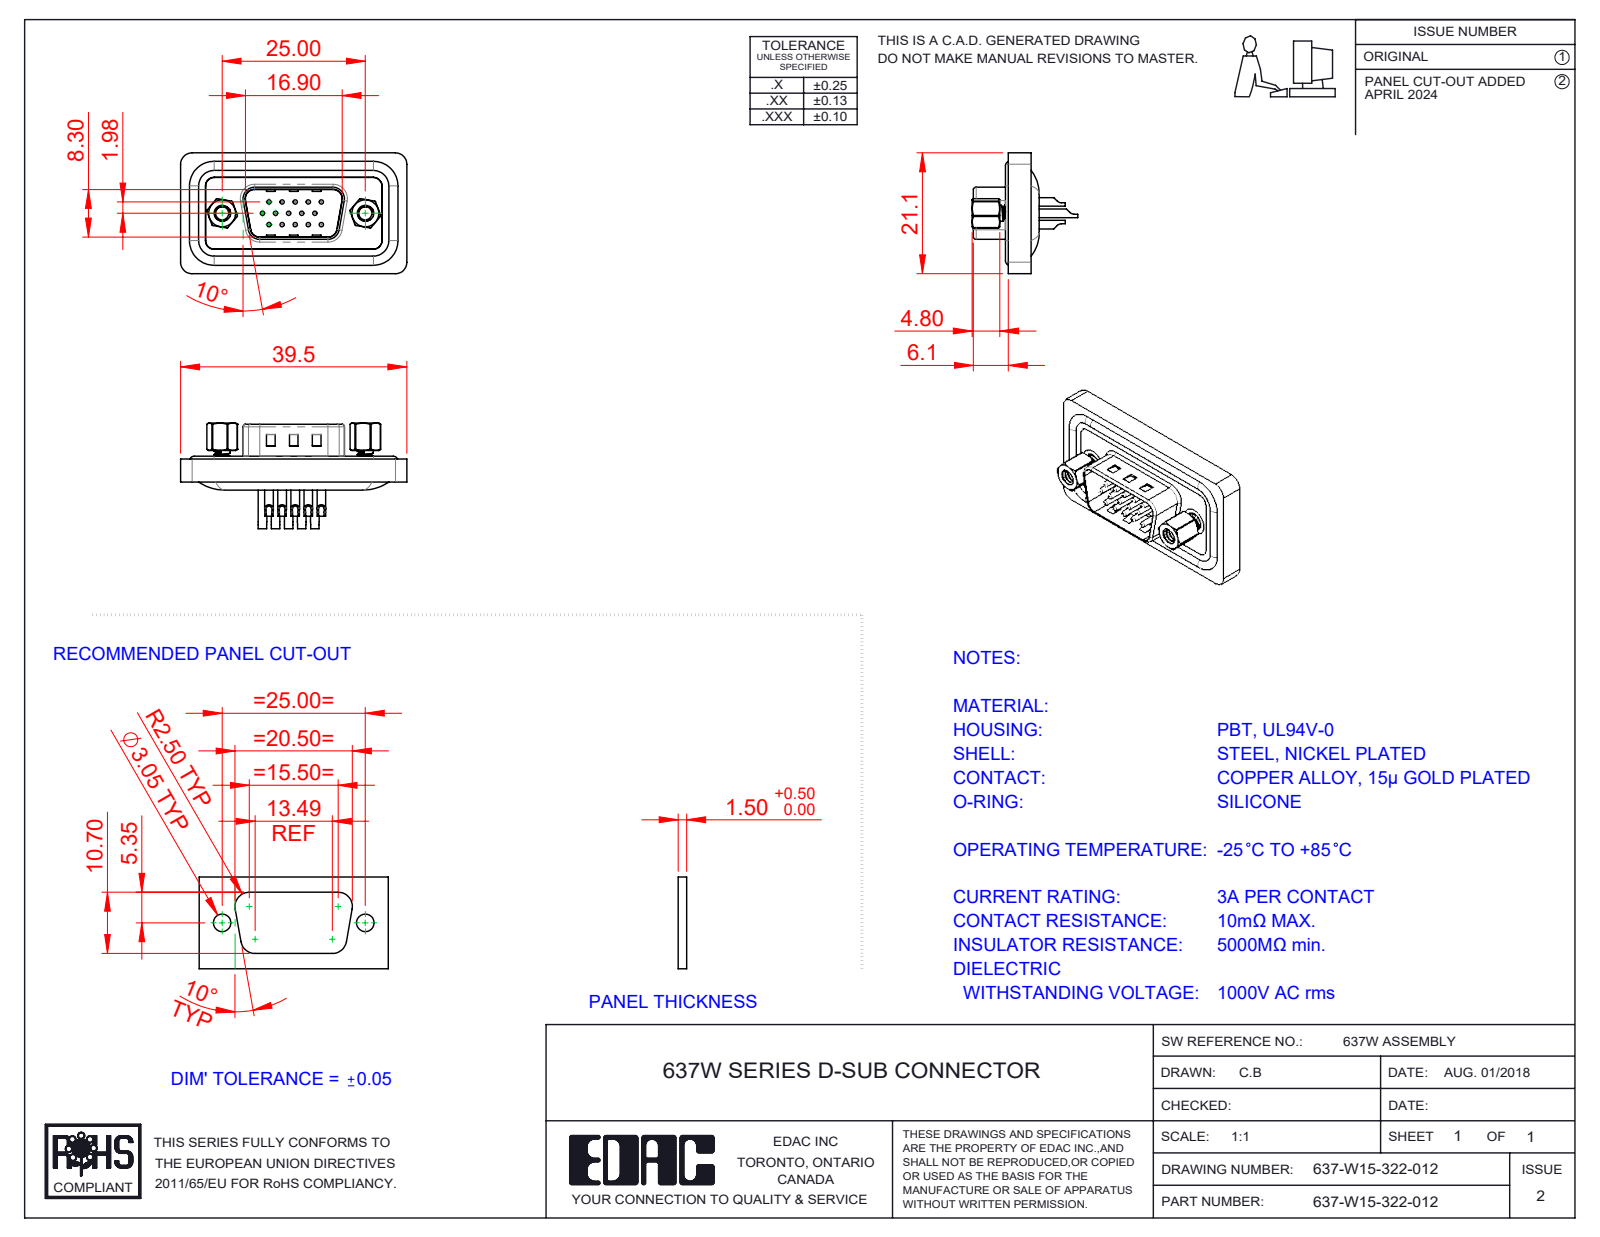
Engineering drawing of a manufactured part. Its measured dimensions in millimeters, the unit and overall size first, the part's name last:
Units: millimetres
Overall size (bounding box): 39.51 × 21.1 × 18.45
Round holes (diameter × count): ⌀0.75 ×15, ⌀1 ×15, ⌀1.5 ×15, ⌀1.6 ×15, ⌀2 ×15, ⌀2.26 ×2, ⌀2.29 ×2, ⌀4 ×2, ⌀4.8 ×2, ⌀5 ×2
Round bosses / shafts (diameter × count): ⌀1.5 ×8, ⌀1.6 ×4, ⌀4.9 ×2, ⌀2.79 ×2, ⌀5 ×1
Partial cylindrical surfaces — rounded edges, fillets, slot ends (radius × count): R1.5 ×14, R2 ×14, R0.5 ×8, R2.7 ×6, R0.9 ×4, R1.6 ×4, R4.3 ×4, R1 ×3
Main face-to-face distances: 0.4, 1.6, 1.1, 2.9, 2.5, 0.5, 4, 3.6, 0.7, 3.4
Hole centre spacings: 3.96, 2.28, 4.57, 2.29, 6.05, 6.04, 7.92, 6.86
Volume: 4 037 mm³ · Surface area: 6 988 mm²
Bodies: 23 solids, 1033 faces (276 planar, 482 cylindrical, 275 other)
Part name (STEP PRODUCT): 637W Contact Row 2_22; 637W Contact Row 3_22; 637W 4-40 Threaded Rivet; 637W Housing_15 Contacts (+5 more)
STEP written by: SolidWorks 2023 (CONFIG_CONTROL_DESIGN)
